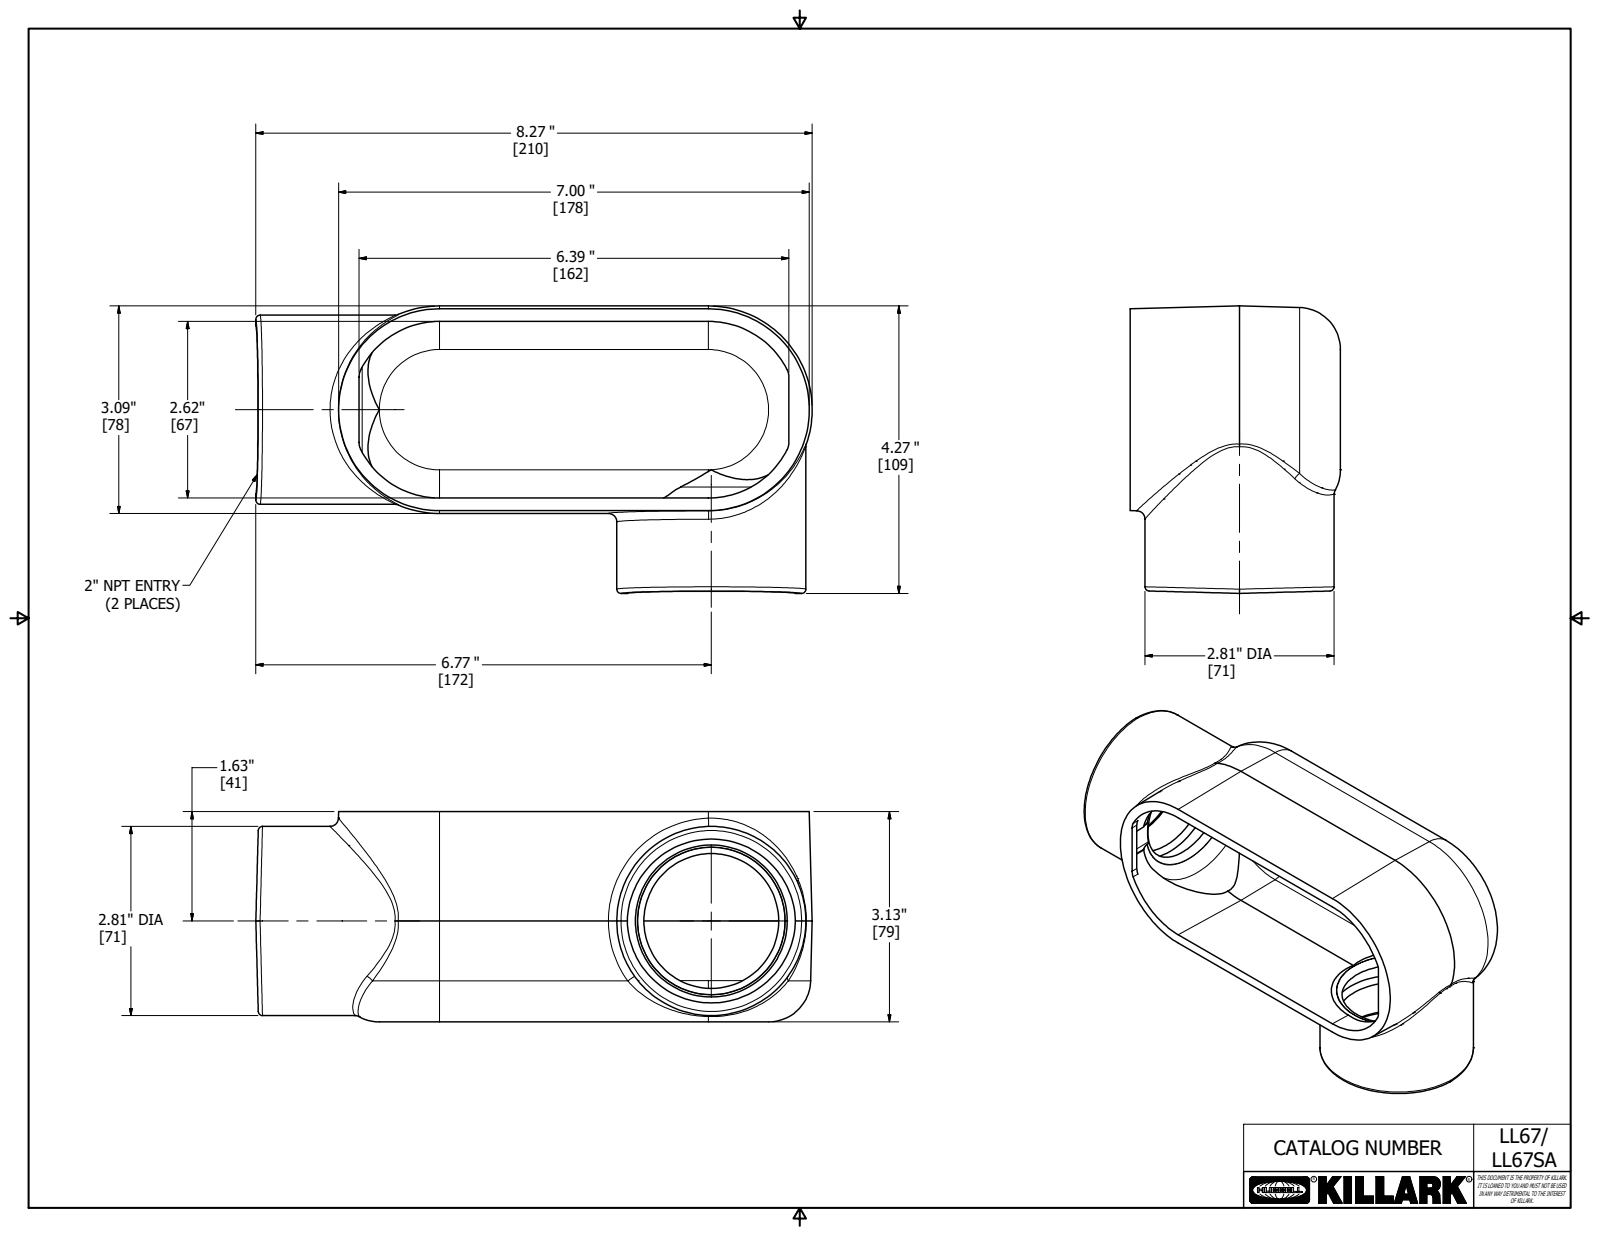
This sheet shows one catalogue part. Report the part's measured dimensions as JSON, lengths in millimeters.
{"part_name": "17709", "step_written_by": "Autodesk Inventor 2018 (AUTOMOTIVE_DESIGN)", "units": "millimeters", "bodies": {"solids": 1, "faces": 102, "planar": 36, "cylindrical": 18, "other": 48}, "overall_size": [210.1, 108.5, 79.4], "volume_mm3": 266800, "surface_area_mm2": 108400, "round_holes": [[60.5, 2], [66.7, 1]], "round_bosses_or_shafts": [[71.4, 2]], "partial_cylinders_radius": [[1.3, 4], [3.2, 4], [11.1, 2], [15.9, 2], [33.3, 1]], "face_to_face_distances": [4.7, 73.6, 68.8, 78.4, 79.4, 74.6, 30.1, 34.9, 103.8, 108.5]}
